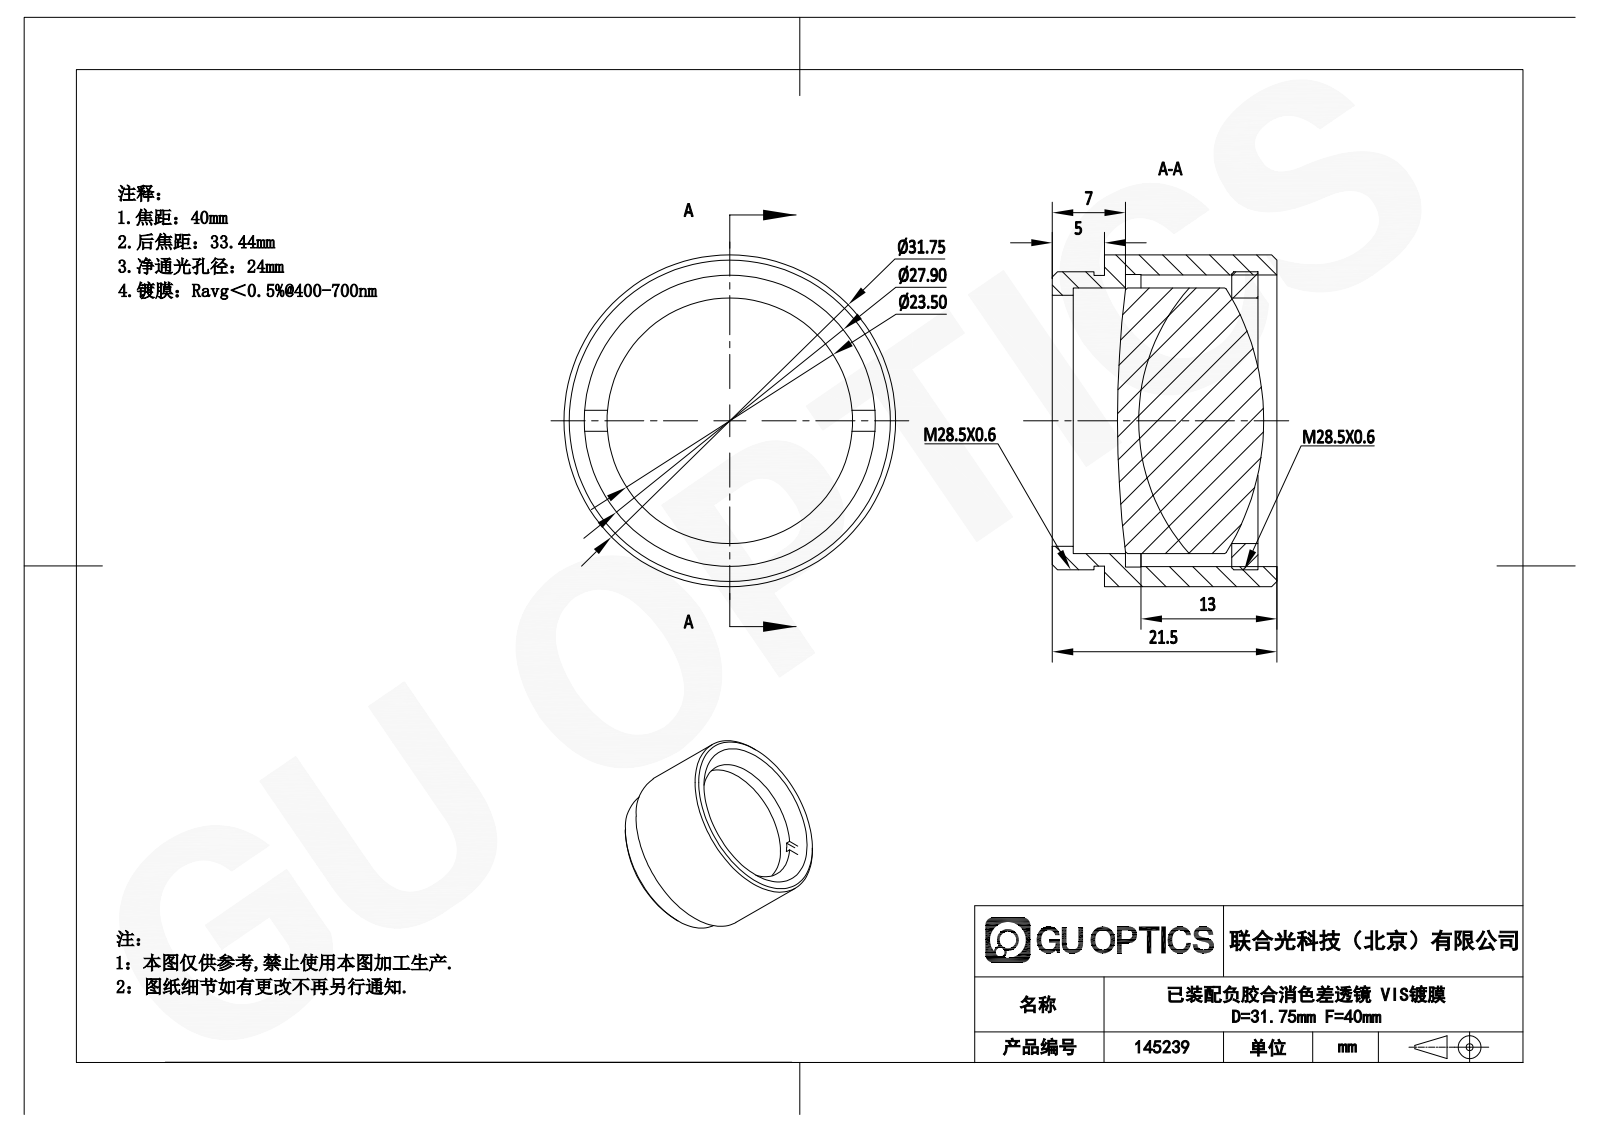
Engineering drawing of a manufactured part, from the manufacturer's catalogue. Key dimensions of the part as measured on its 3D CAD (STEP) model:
Part name (STEP PRODUCT): APD-ML25-040-VIS; M28.5x0.6ѹȦ; GL31-025B-040-VIS_Solidworks
STEP written by: SolidWorks 2022 (AUTOMOTIVE_DESIGN)
Units: millimetres
Bodies: 4 solids, 56 faces (16 planar, 22 cylindrical, 18 other)
Overall size (bounding box): 31.76 × 31.76 × 21.5
Volume: 9 463 mm³ · Surface area: 8 201 mm²
Round holes (diameter × count): ⌀23.5 ×1, ⌀24 ×1, ⌀27.9 ×1, ⌀28 ×1
Round bosses / shafts (diameter × count): ⌀31.76 ×1, ⌀28.5 ×1, ⌀27.8 ×1, ⌀25.4 ×1
Main face-to-face distances: 2, 5, 2.5, 10, 12.5, 17.5, 4, 15, 6.5, 21.5
